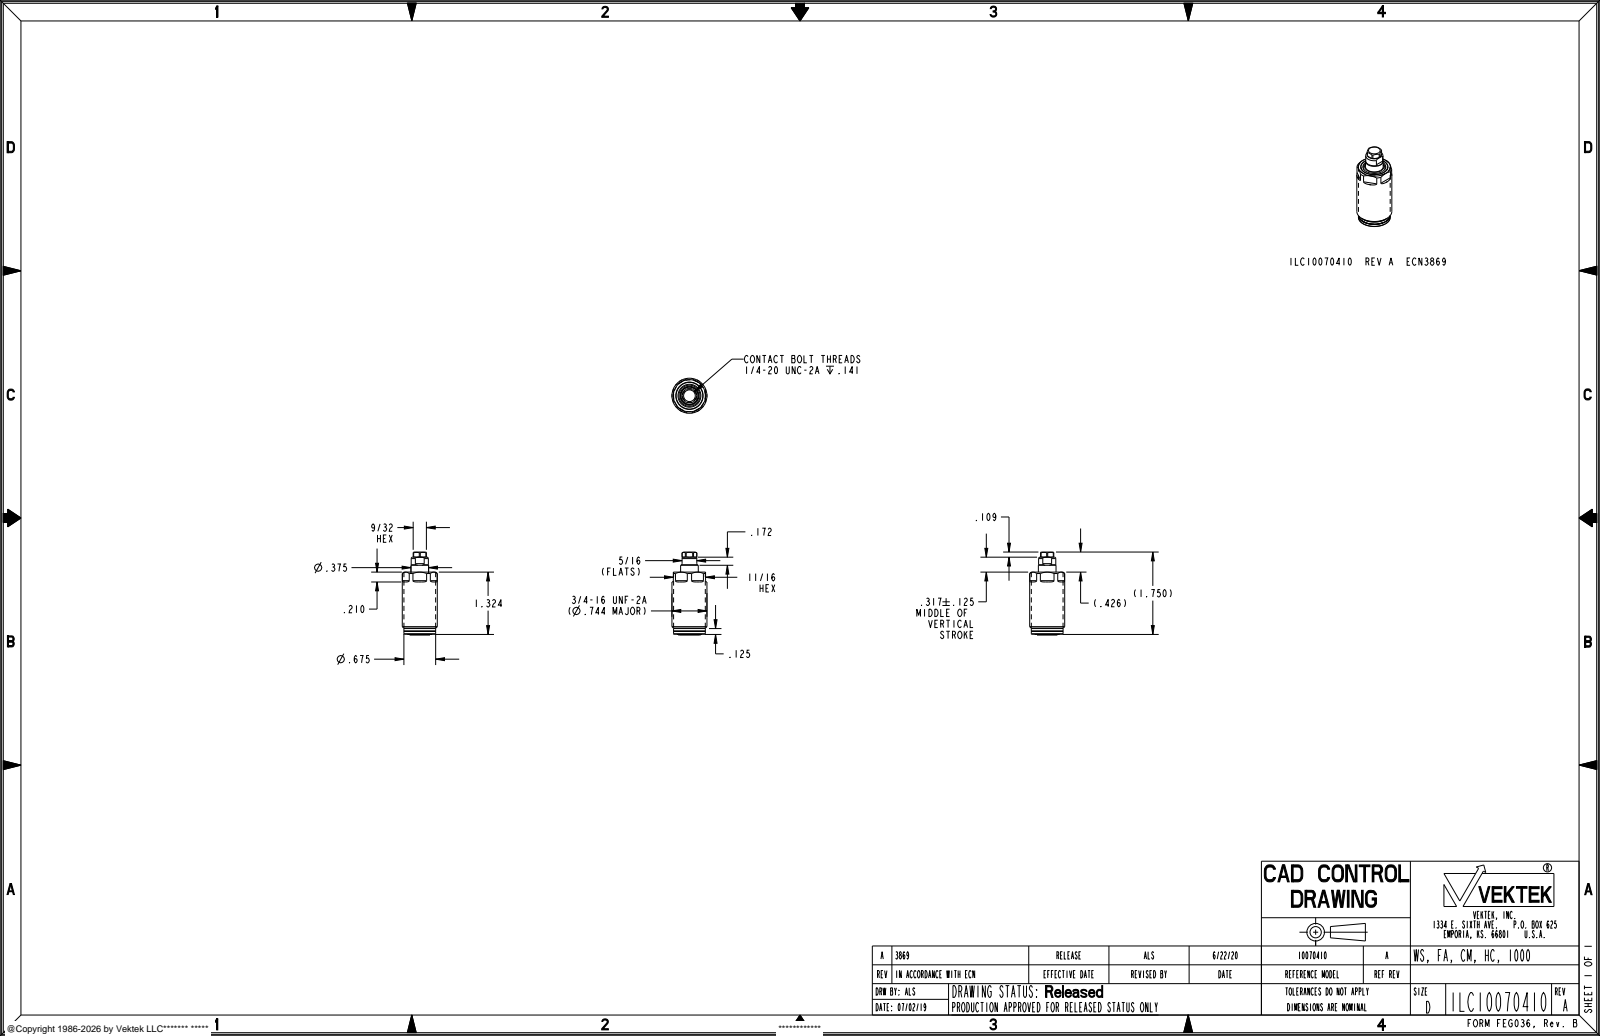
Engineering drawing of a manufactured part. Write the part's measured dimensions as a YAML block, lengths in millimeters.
part_name: "ILC10070410"
step_written_by: "PRO/ENGINEER BY PARAMETRIC TECHNOLOGY CORPORATION, 2013320 (CONFIG_CONTROL_DESIGN)"
units: millimeters
bodies: {solids: 1, faces: 109, planar: 34, cylindrical: 38, other: 37}
overall_size: [44.8, 18.9, 18.9]
volume: 9470
surface_area: 5085
round_holes:
  - {diameter: 10, count: 1}
  - {diameter: 12.4, count: 1}
  - {diameter: 12.5, count: 1}
  - {diameter: 14.3, count: 1}
round_bosses_or_shafts:
  - {diameter: 18.9, count: 1}
  - {diameter: 17.1, count: 1}
  - {diameter: 17.1, count: 1}
  - {diameter: 14.4, count: 1}
  - {diameter: 13.3, count: 1}
  - {diameter: 9.5, count: 1}
partial_cylinders:
  - {radius: 0.7, count: 6}
  - {radius: 0.9, count: 2}
  - {radius: 4, count: 1}
  - {radius: 4.6, count: 1}
face_to_face_distances: [2.4, 17.4, 30.1, 32.5, 1, 31.1, 33.5, 31.2, 30.2, 2.3]
